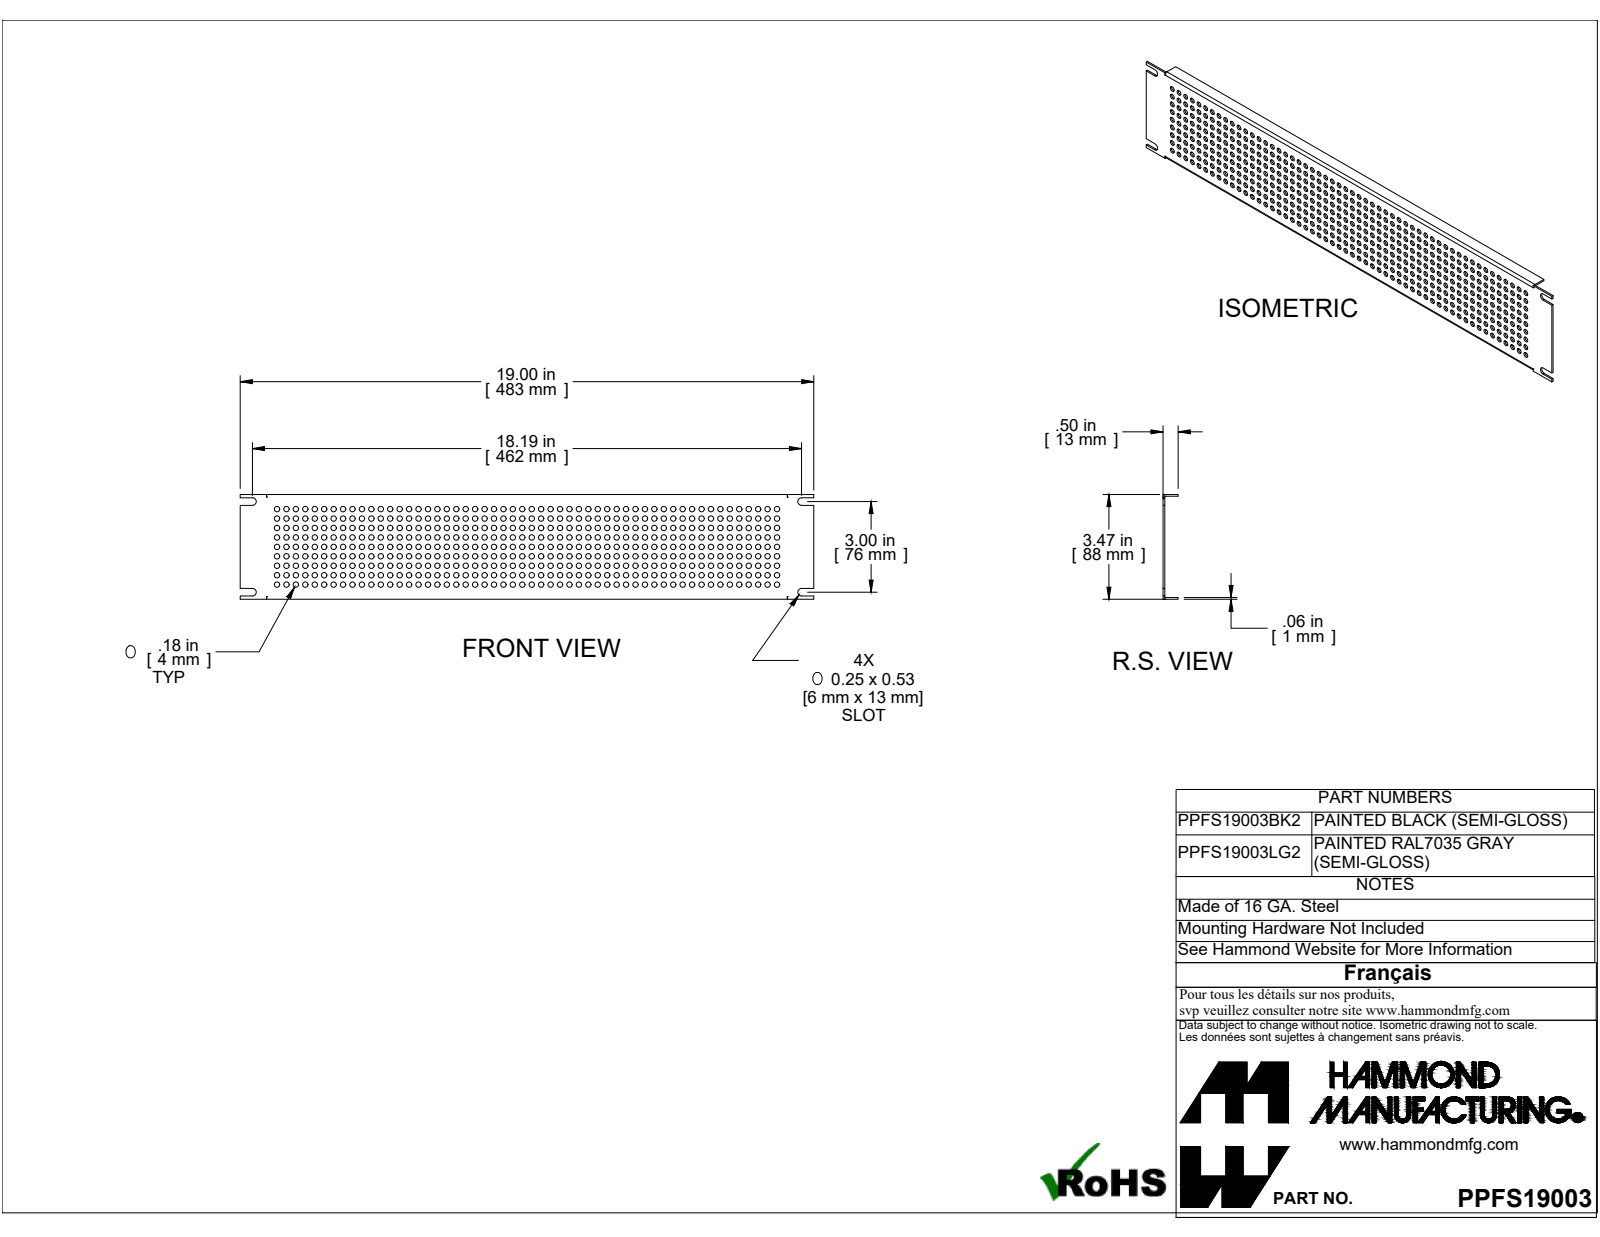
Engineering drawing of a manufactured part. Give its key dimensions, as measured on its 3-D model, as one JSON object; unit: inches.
{"part_name": "PPFS19003LG2", "step_written_by": "SolidWorks 2019 (CONFIG_CONTROL_DESIGN)", "units": "inches", "bodies": {"solids": 1, "faces": 532, "planar": 38, "cylindrical": 494, "other": 0}, "overall_size": [19, 3.468, 0.5], "volume_in3": 3.868, "surface_area_in2": 154, "round_holes": [[0.177, 486]], "partial_cylinders_radius": [[0.125, 4], [0.029, 2], [0.086, 2]], "face_to_face_distances": [0.057, 0.057, 3.411, 3.468, 3.354, 0.5, 0.443, 19, 0.875, 18.125], "hole_center_spacings": [0.699, 0.313, 0.442, 1.289, 0.988, 0.625, 0.937, 1.127]}
